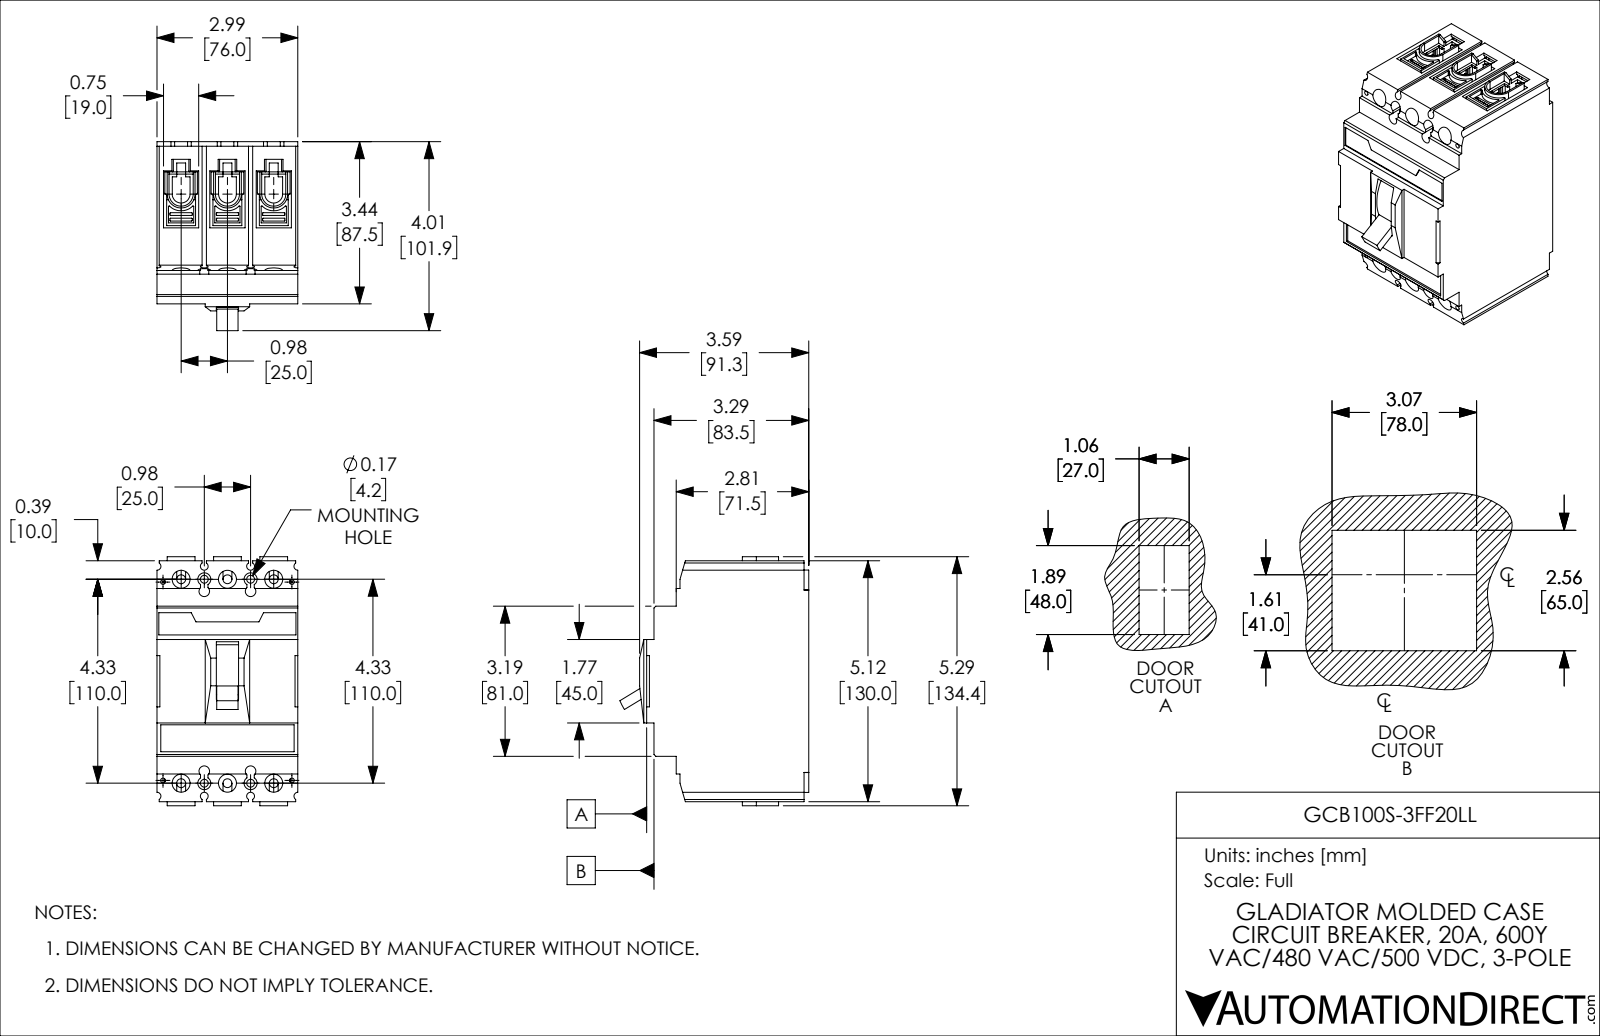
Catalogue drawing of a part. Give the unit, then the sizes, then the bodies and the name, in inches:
Units: inches
Overall size (bounding box): 5.291 × 4.013 × 2.992
Round holes (diameter × count): ⌀0.165 ×8, ⌀0.189 ×6, ⌀0.382 ×6, ⌀0.098 ×4, ⌀0.276 ×4
Partial cylindrical surfaces — rounded edges, fillets, slot ends (radius × count): R0.012 ×86, R0.02 ×38, R0.039 ×14, R0.157 ×14, R0.024 ×6, R0.083 ×4, R0.112 ×4, R0.189 ×3
Main face-to-face distances: 2.992, 0.984, 0.622, 4.496, 1.732, 0.11, 3.445, 0.748, 1.969, 5.118
Hole centre spacings: 0.492, 0.564, 0.984, 4.359, 4.633, 4.441, 4.331, 0.276
Volume: 43.23 in³ · Surface area: 148.5 in²
Bodies: 1 solid, 1256 faces (784 planar, 424 cylindrical, 48 other)
Part name (STEP PRODUCT): GCB100S-3FF20LL
STEP written by: SolidWorks 2021 (CONFIG_CONTROL_DESIGN)
